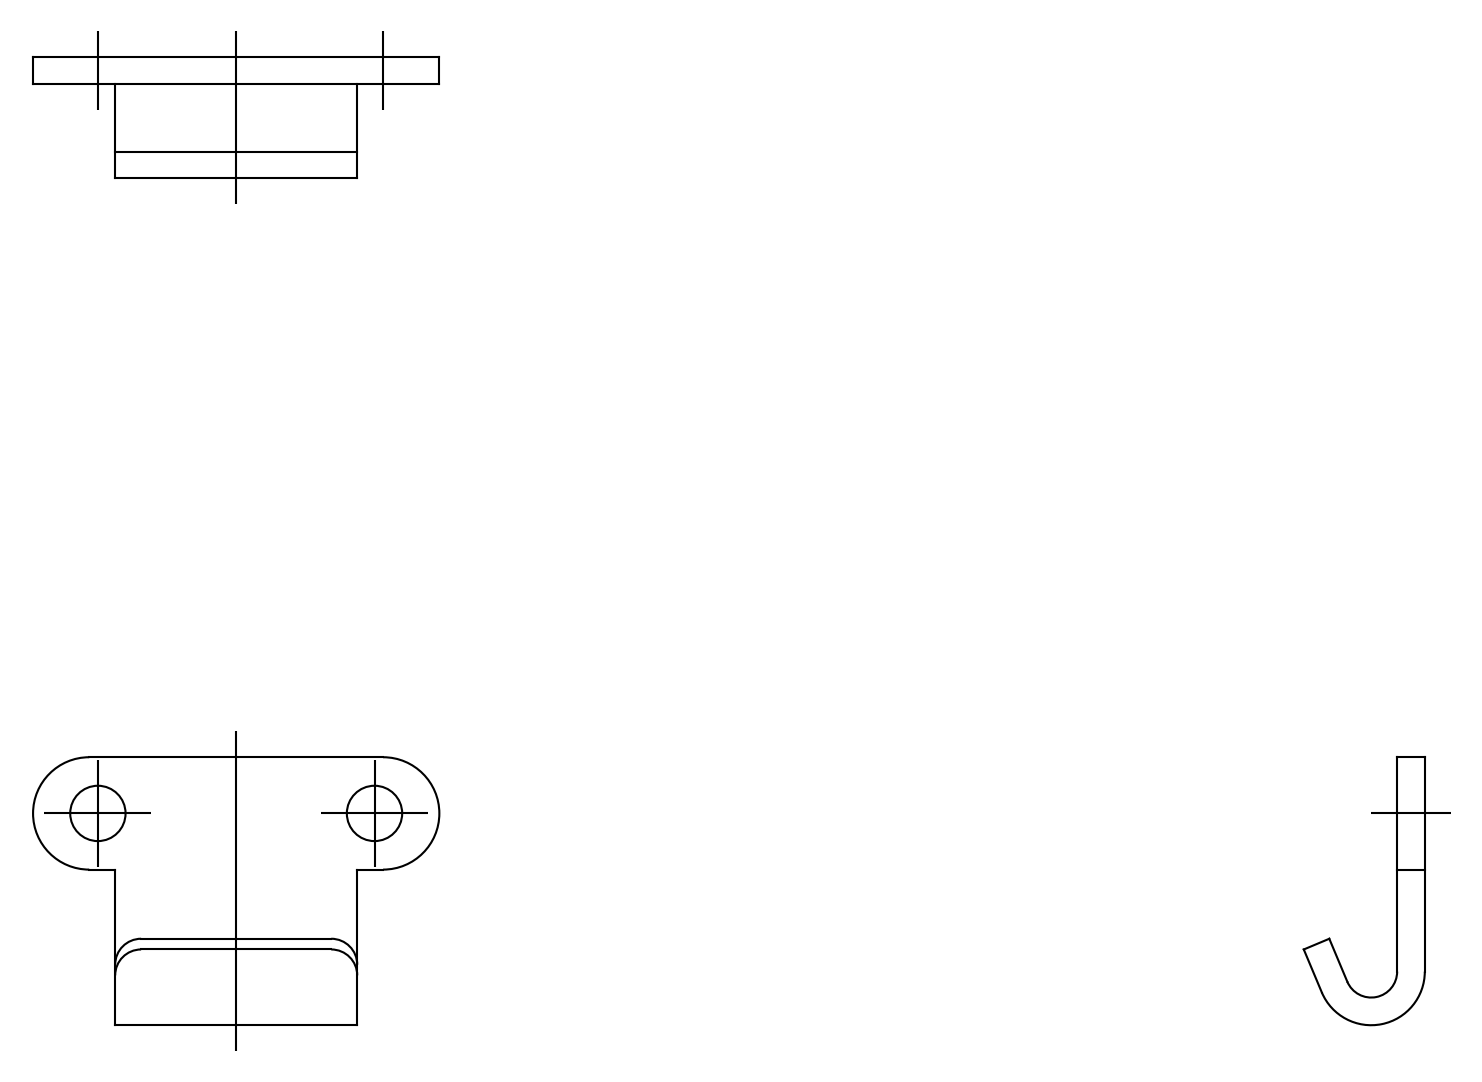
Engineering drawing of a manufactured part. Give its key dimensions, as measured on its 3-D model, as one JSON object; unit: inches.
{"step_written_by": "spGate 18.9.1 (****-****-****-****) (AUTOMOTIVE_DESIGN)", "units": "inches", "bodies": {"solids": 1, "faces": 20, "planar": 10, "cylindrical": 10, "other": 0}, "overall_size": [0.925, 0.61, 0.315], "volume_in3": 0.033, "surface_area_in2": 1.32, "round_holes": [[0.126, 2]], "partial_cylinders_radius": [[0.059, 3], [0.128, 2], [0.122, 1]], "face_to_face_distances": [0.063, 0.551, 0.256], "hole_center_spacings": [0.63]}
